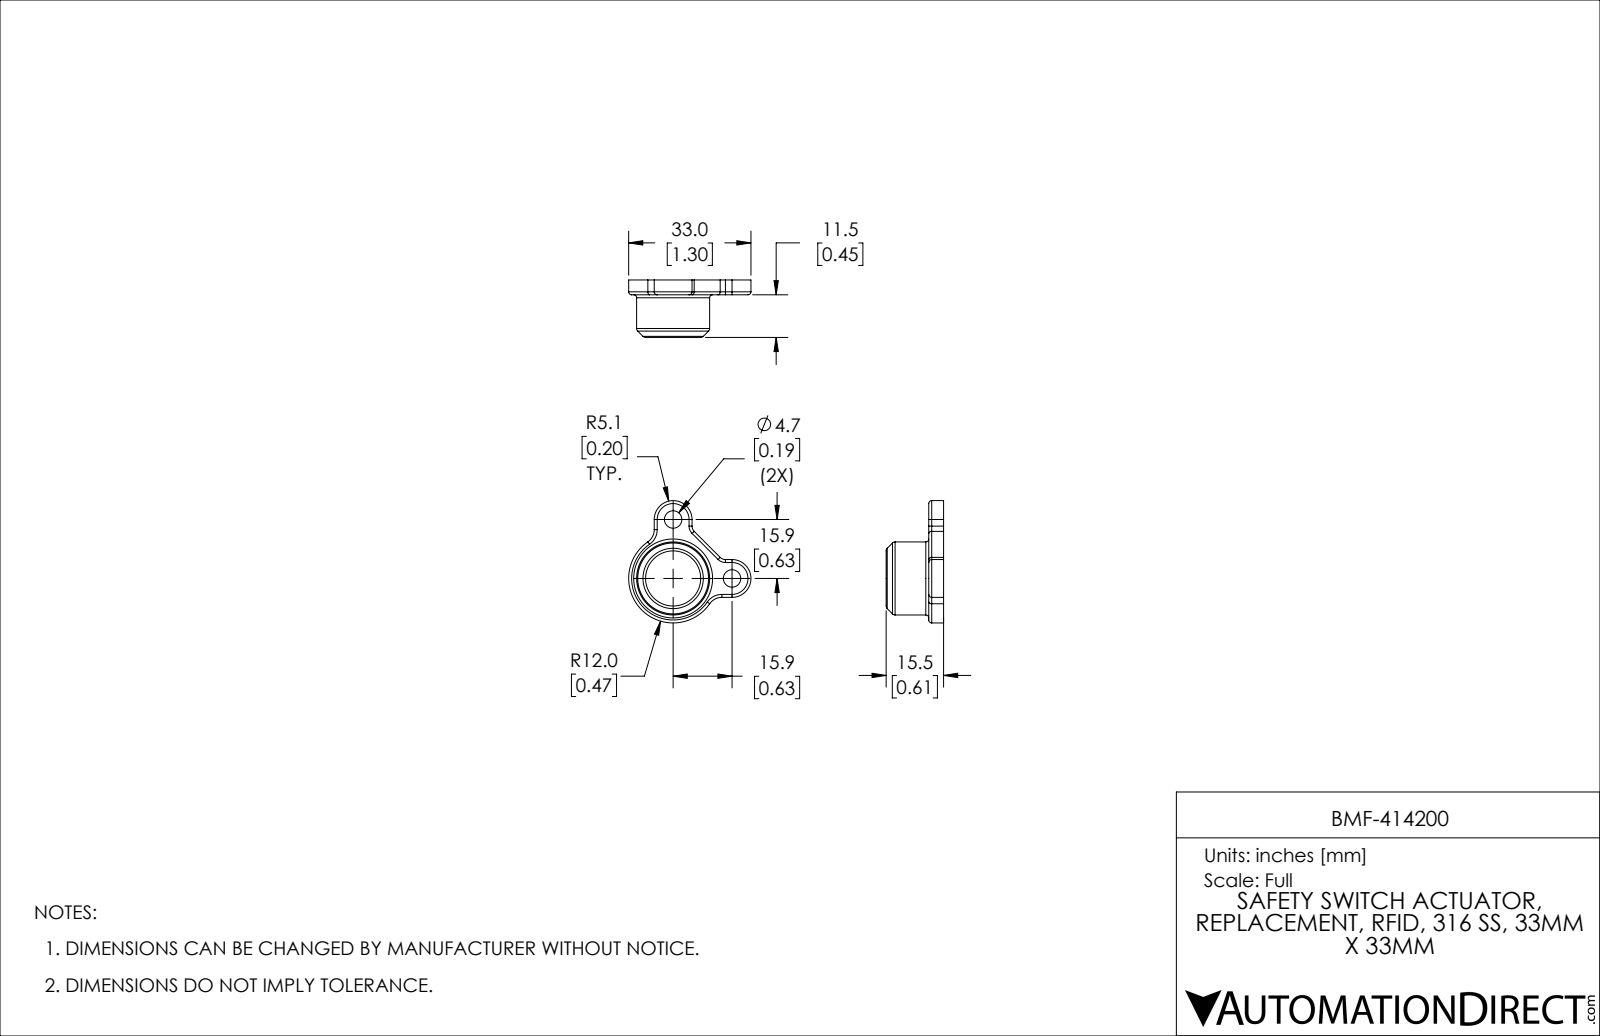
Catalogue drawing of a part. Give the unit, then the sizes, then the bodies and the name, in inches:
Units: inches
Overall size (bounding box): 1.299 × 1.299 × 0.61
Round holes (diameter × count): ⌀0.098 ×4, ⌀0.185 ×2, ⌀0.079 ×1, ⌀0.528 ×1, ⌀0.63 ×1, ⌀0.709 ×1
Round bosses / shafts (diameter × count): ⌀0.776 ×1, ⌀0.622 ×1
Partial cylindrical surfaces — rounded edges, fillets, slot ends (radius × count): R0.031 ×5, R0.079 ×2, R0.157 ×2, R0.201 ×2, R0.472 ×1
Main face-to-face distances: 0.059, 0.539, 0.61, 0.598, 0.157, 0.146, 0.453, 0.071, 0.087, 0.551
Hole centre spacings: 0.191, 0.481, 0.217, 0.626, 0.68, 0.698, 0.871, 0.509
Volume: 0.22 in³ · Surface area: 6.378 in²
Bodies: 2 solids, 68 faces (19 planar, 25 cylindrical, 24 other)
Part name (STEP PRODUCT): BMF-414200
STEP written by: SolidWorks 2019 (AUTOMOTIVE_DESIGN)
